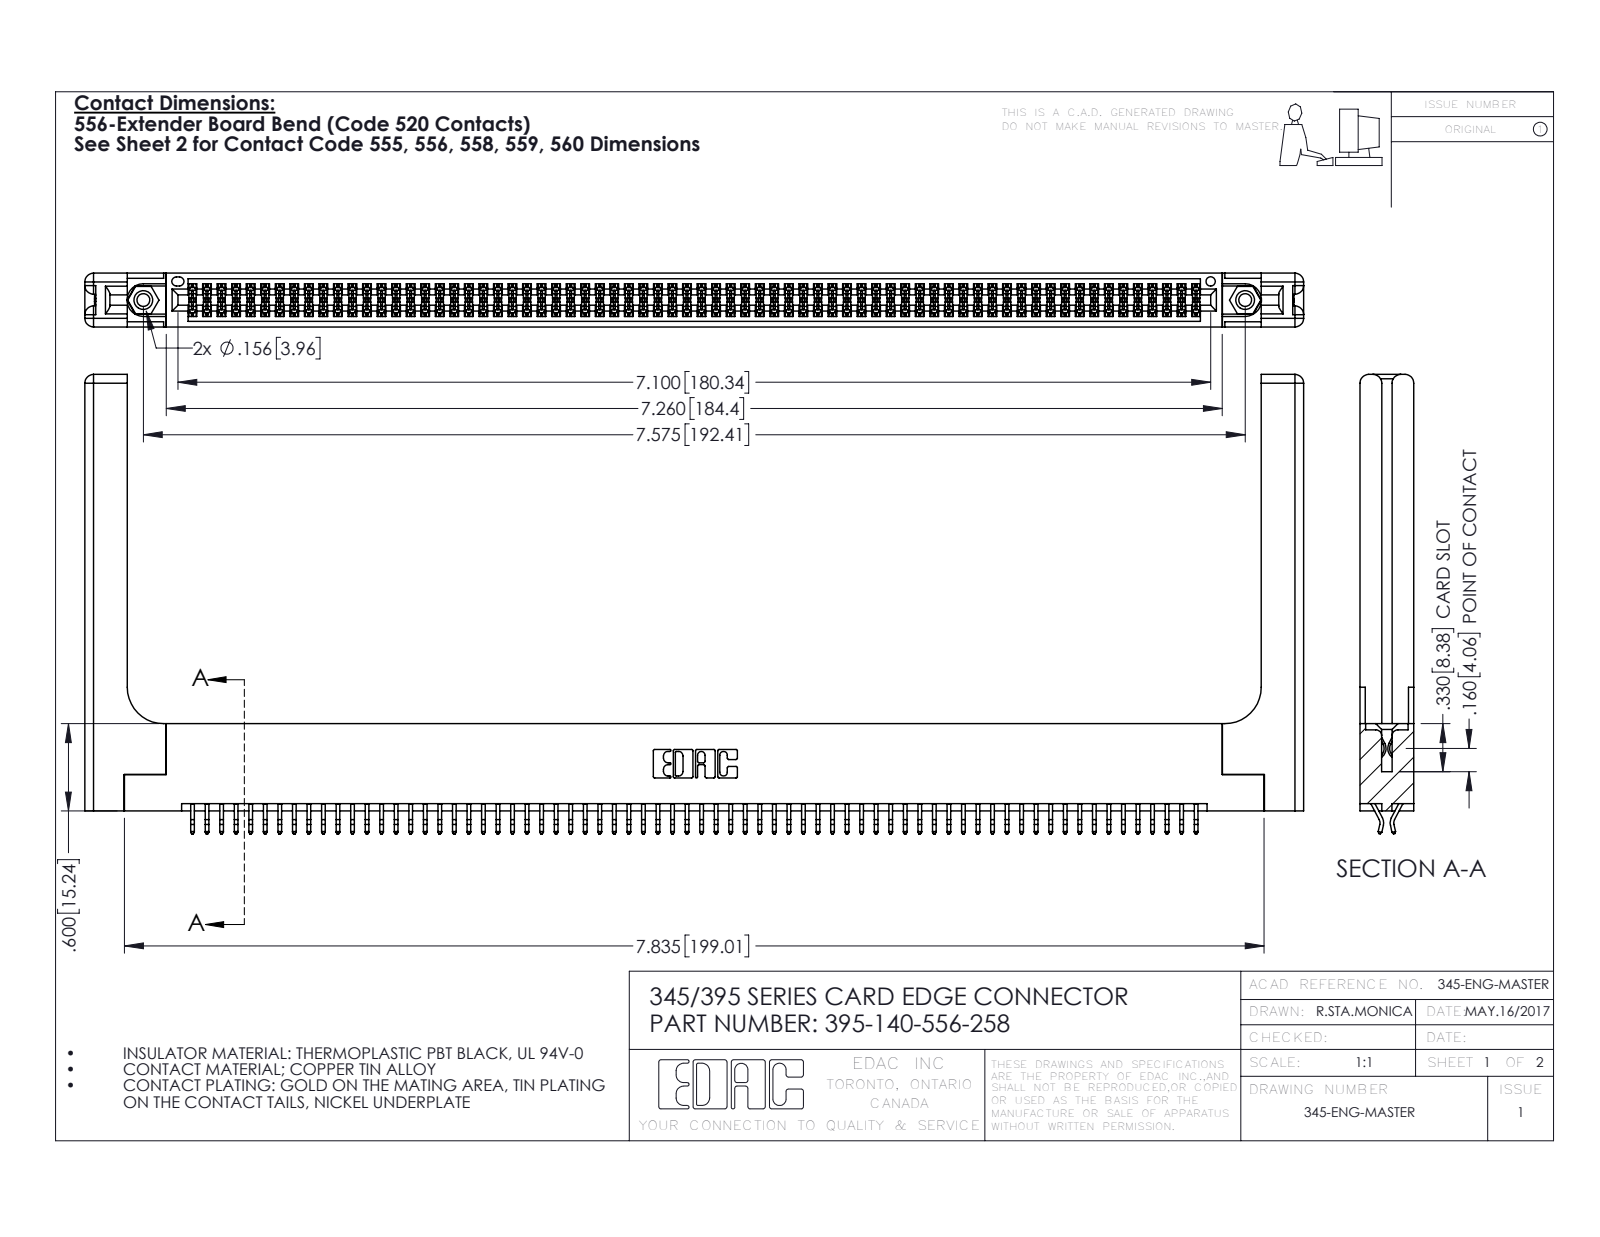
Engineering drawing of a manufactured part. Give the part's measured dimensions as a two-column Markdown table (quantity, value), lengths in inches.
| quantity | value |
| --- | --- |
| part name | 395-140-556-258; 345 Part_Flush Mounting Lugs - 0.156 Dia-TH; 345-250-001_345-250-001-102; 345-220-058_345-220-058 (+1 more) |
| STEP written by | SolidWorks 2016 (CONFIG_CONTROL_DESIGN) |
| units | inches |
| bodies | 145 solids, 8222 faces (5408 planar, 2754 cylindrical, 60 other) |
| overall size | 8.379 × 3.157 × 0.37 |
| volume | 1.794 in³ |
| surface area | 56.44 in² |
| round holes (diameter × count) | 0.089 × 2, 0.125 × 2, 0.156 × 2, 0.064 × 1 |
| round bosses / shafts (diameter × count) | 0.155 × 2 |
| partial cylindrical surfaces (radius × count) | 0.006 × 210, 0.01 × 22, 0.06 × 16, 0.007 × 6, 0.031 × 6, 0.026 × 3, 0.01 × 2, 0.014 × 2 |
| main face-to-face distances | 0.072, 0.298, 0.37, 0.2, 0.025, 0.098, 0.272, 0.225, 0.148, 0.15 |
| hole center spacings | 0.27, 7.339, 7.575 |
